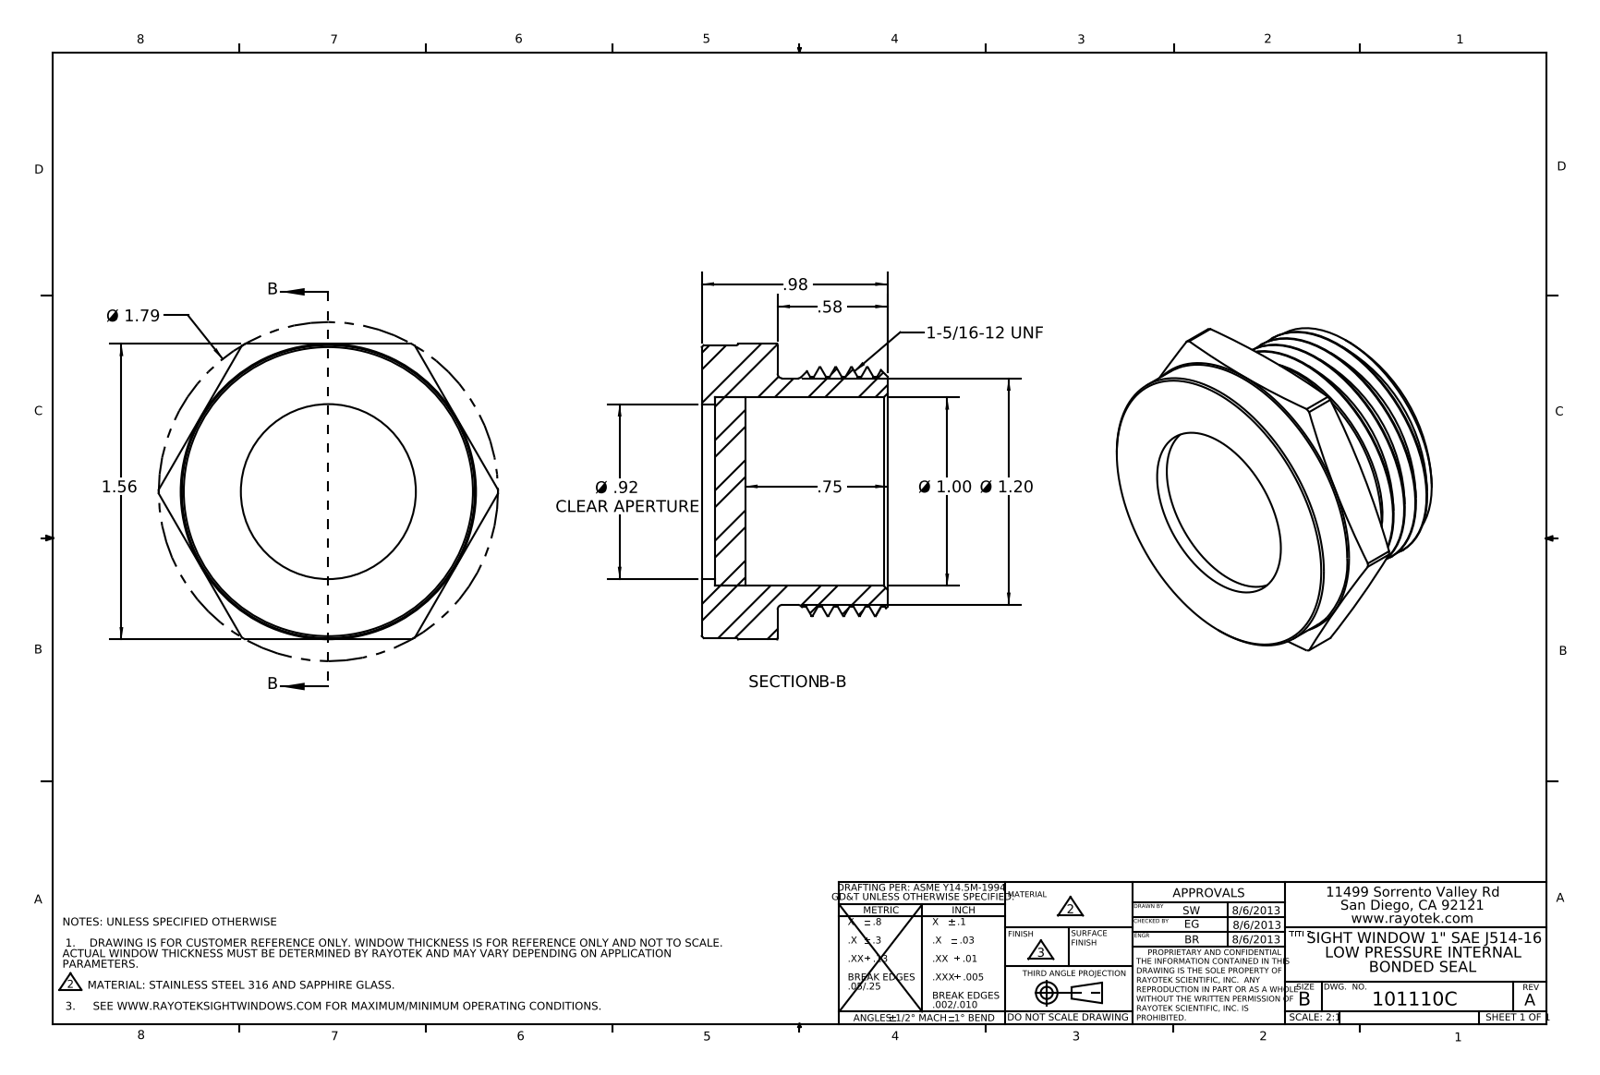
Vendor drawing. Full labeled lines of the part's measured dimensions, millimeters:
Part name (STEP PRODUCT): 403110
STEP written by: SolidWorks 2012 (AUTOMOTIVE_DESIGN)
Units: millimetres
Bodies: 2 solids, 61 faces (12 planar, 26 cylindrical, 23 other)
Overall size (bounding box): 45.4 × 39.6 × 24.9
Volume: 14 100 mm³ · Surface area: 8 561 mm²
Round holes (diameter × count): ⌀23.4 ×1, ⌀25.3 ×1
Round bosses / shafts (diameter × count): ⌀39.2 ×1, ⌀33.4 ×1, ⌀30.4 ×1
Partial cylindrical surfaces — rounded edges, fillets, slot ends (radius × count): R22.7 ×1
Main face-to-face distances: 1.8, 4, 5.8, 4.3, 8.3, 10.2, 39.6, 14.7, 19.1, 23.1
